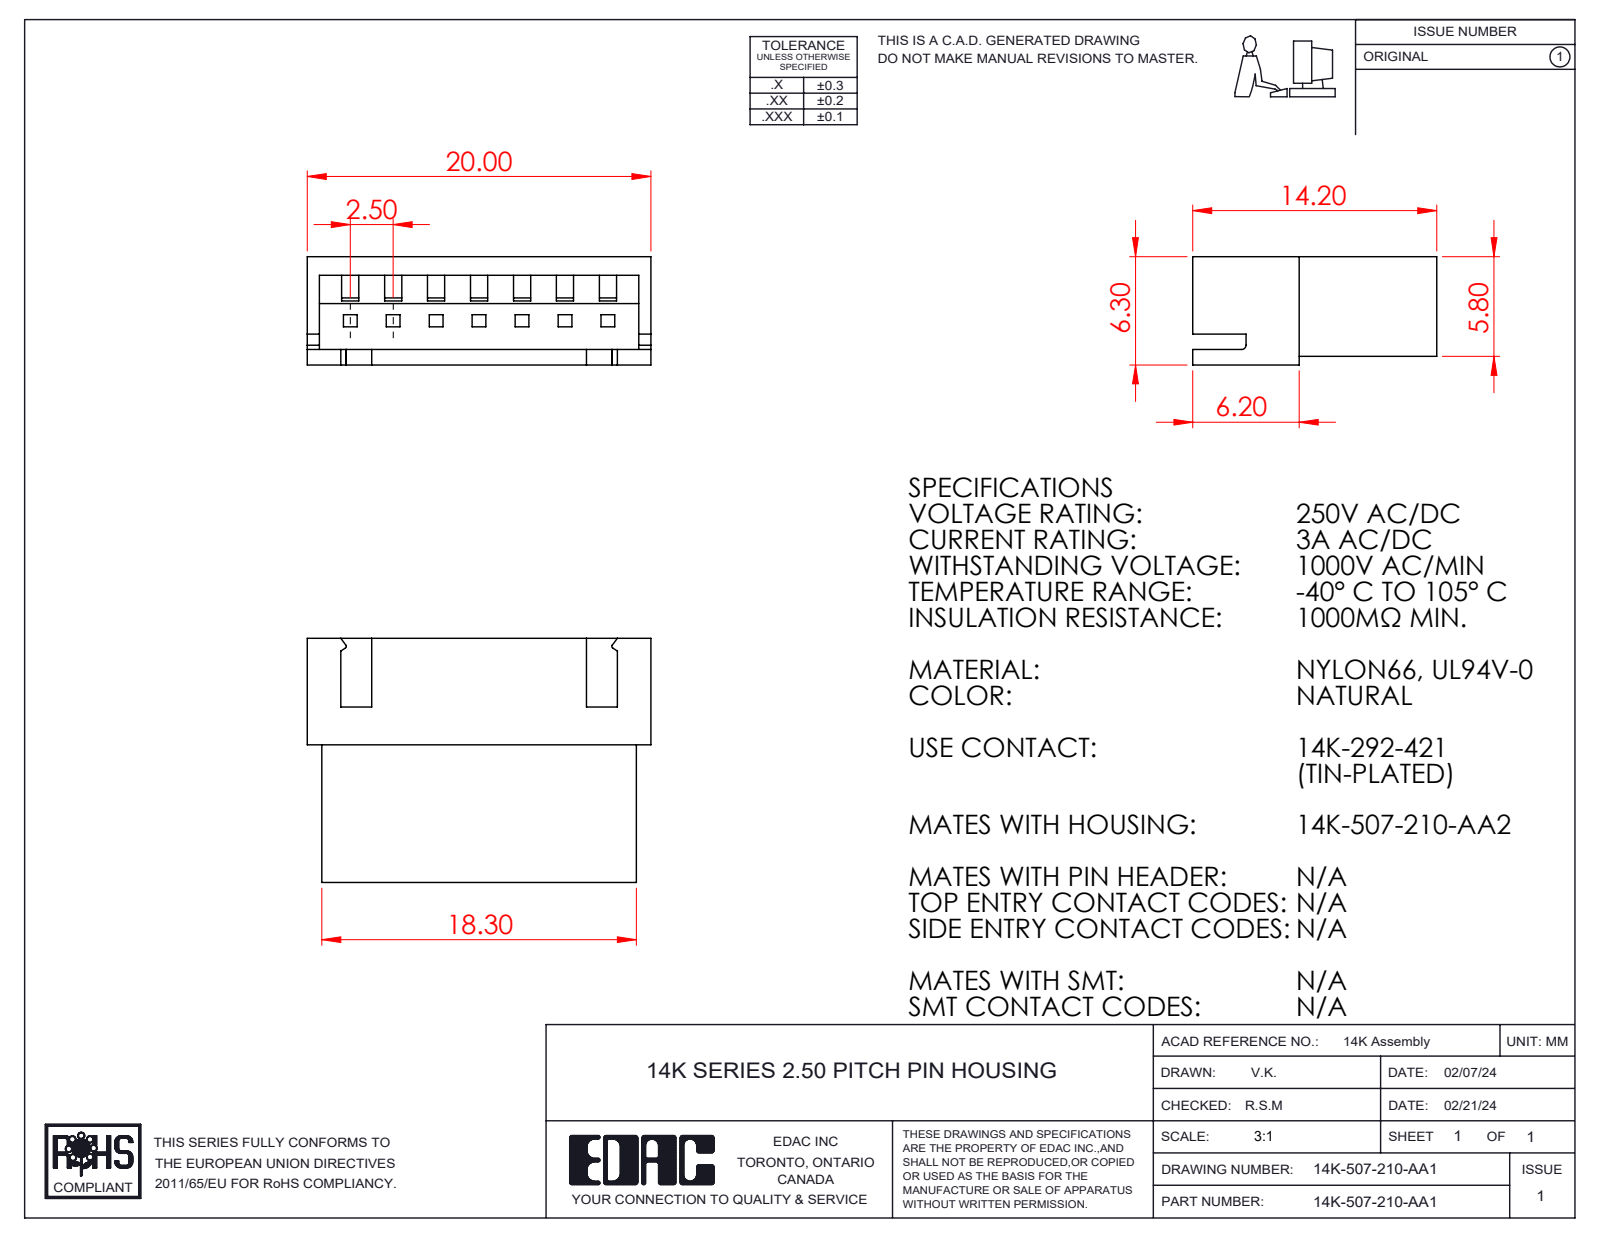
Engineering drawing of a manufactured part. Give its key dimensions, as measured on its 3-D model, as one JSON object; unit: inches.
{"part_name": "14K-507-210-AA1", "step_written_by": "SolidWorks 2023 (CONFIG_CONTROL_DESIGN)", "units": "inches", "bodies": {"solids": 1, "faces": 214, "planar": 210, "cylindrical": 4, "other": 0}, "overall_size": [0.787, 0.559, 0.248], "volume_in3": 0.052, "surface_area_in2": 3.018, "partial_cylinders_radius": [[0.004, 2], [0.01, 1]], "face_to_face_distances": [0.02, 0.098, 0.197, 0.228, 0.035, 0.118, 0.295, 0.079, 0.177, 0.394]}
